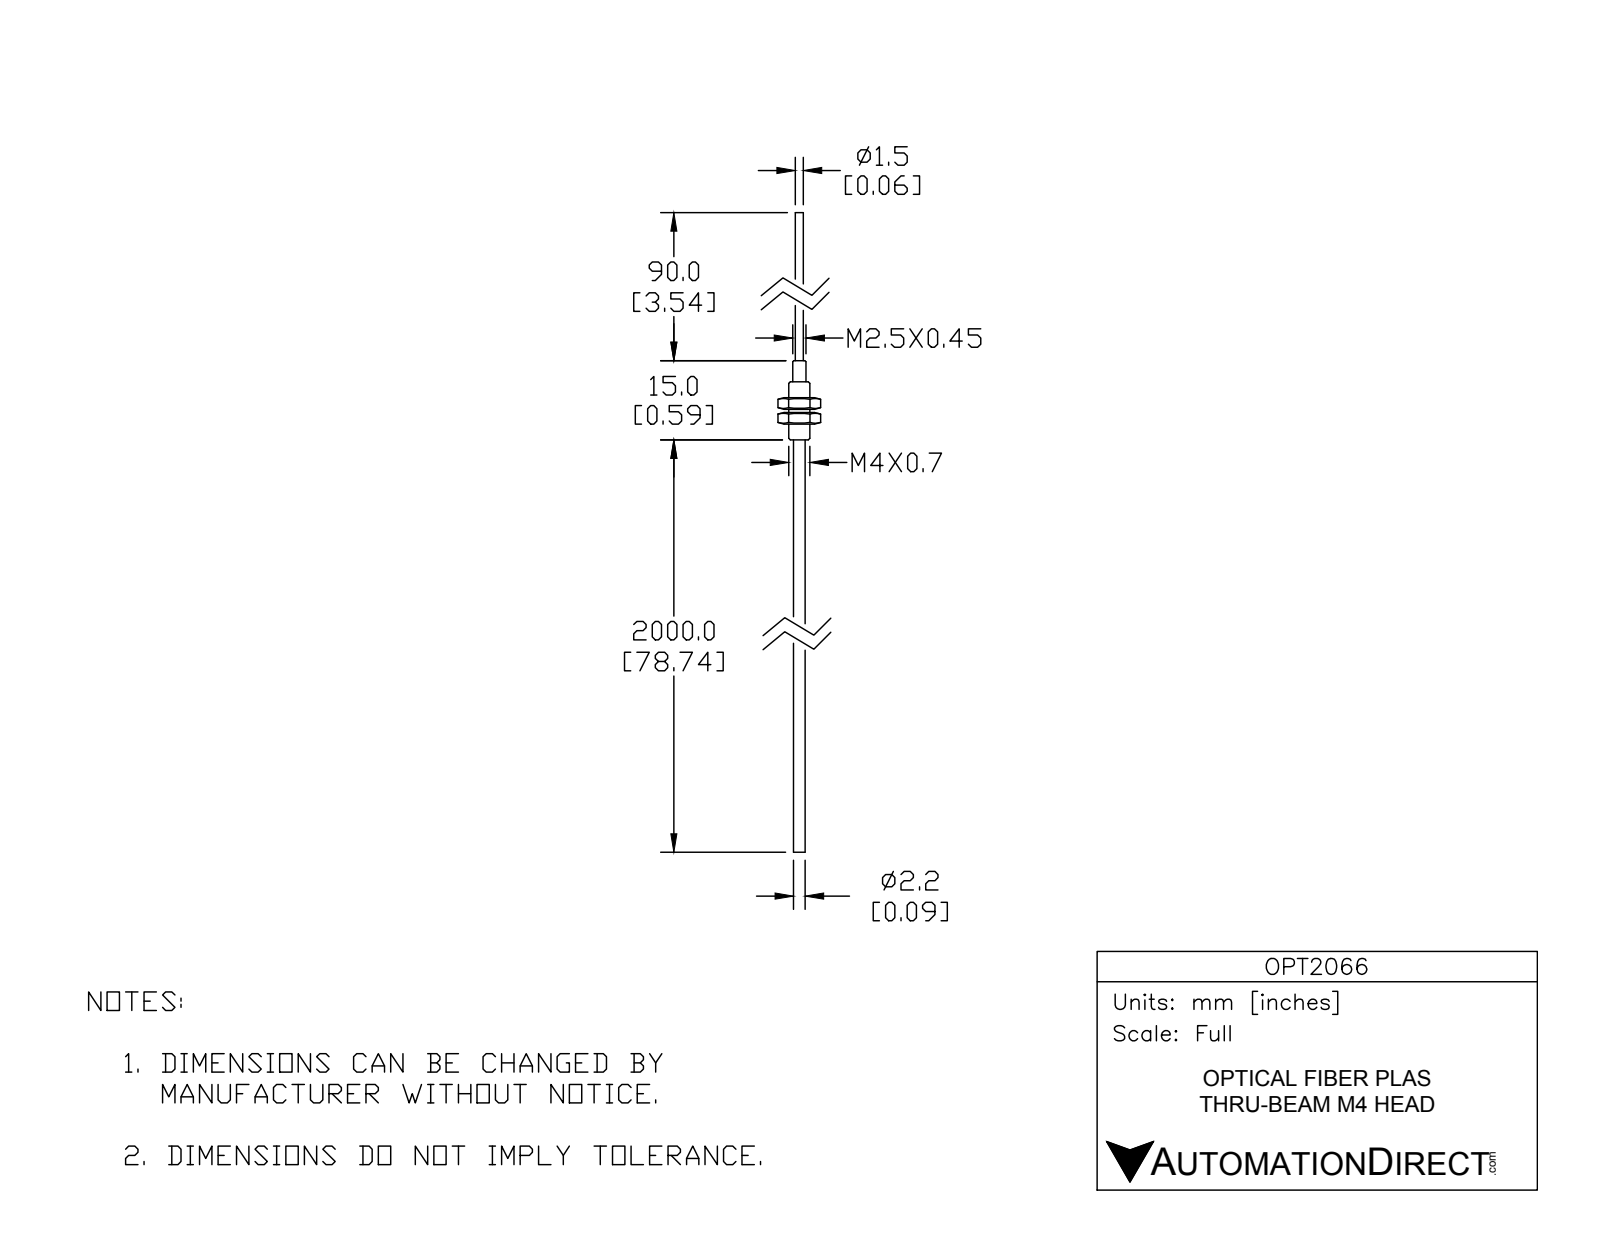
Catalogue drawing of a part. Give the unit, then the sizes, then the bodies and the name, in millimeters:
Units: millimetres
Overall size (bounding box): 121 × 8.1 × 7
Round bosses / shafts (diameter × count): ⌀4 ×1, ⌀2.5 ×1, ⌀2.2 ×1, ⌀1.5 ×1
Main face-to-face distances: 7, 2.2, 2.8, 5, 0.6, 3, 5.2, 5.8, 8, 11
Volume: 590 mm³ · Surface area: 943 mm²
Bodies: 3 solids, 55 faces (25 planar, 16 cylindrical, 14 other)
Part name (STEP PRODUCT): OPT2066
STEP written by: SolidWorks 2014 (AUTOMOTIVE_DESIGN)
